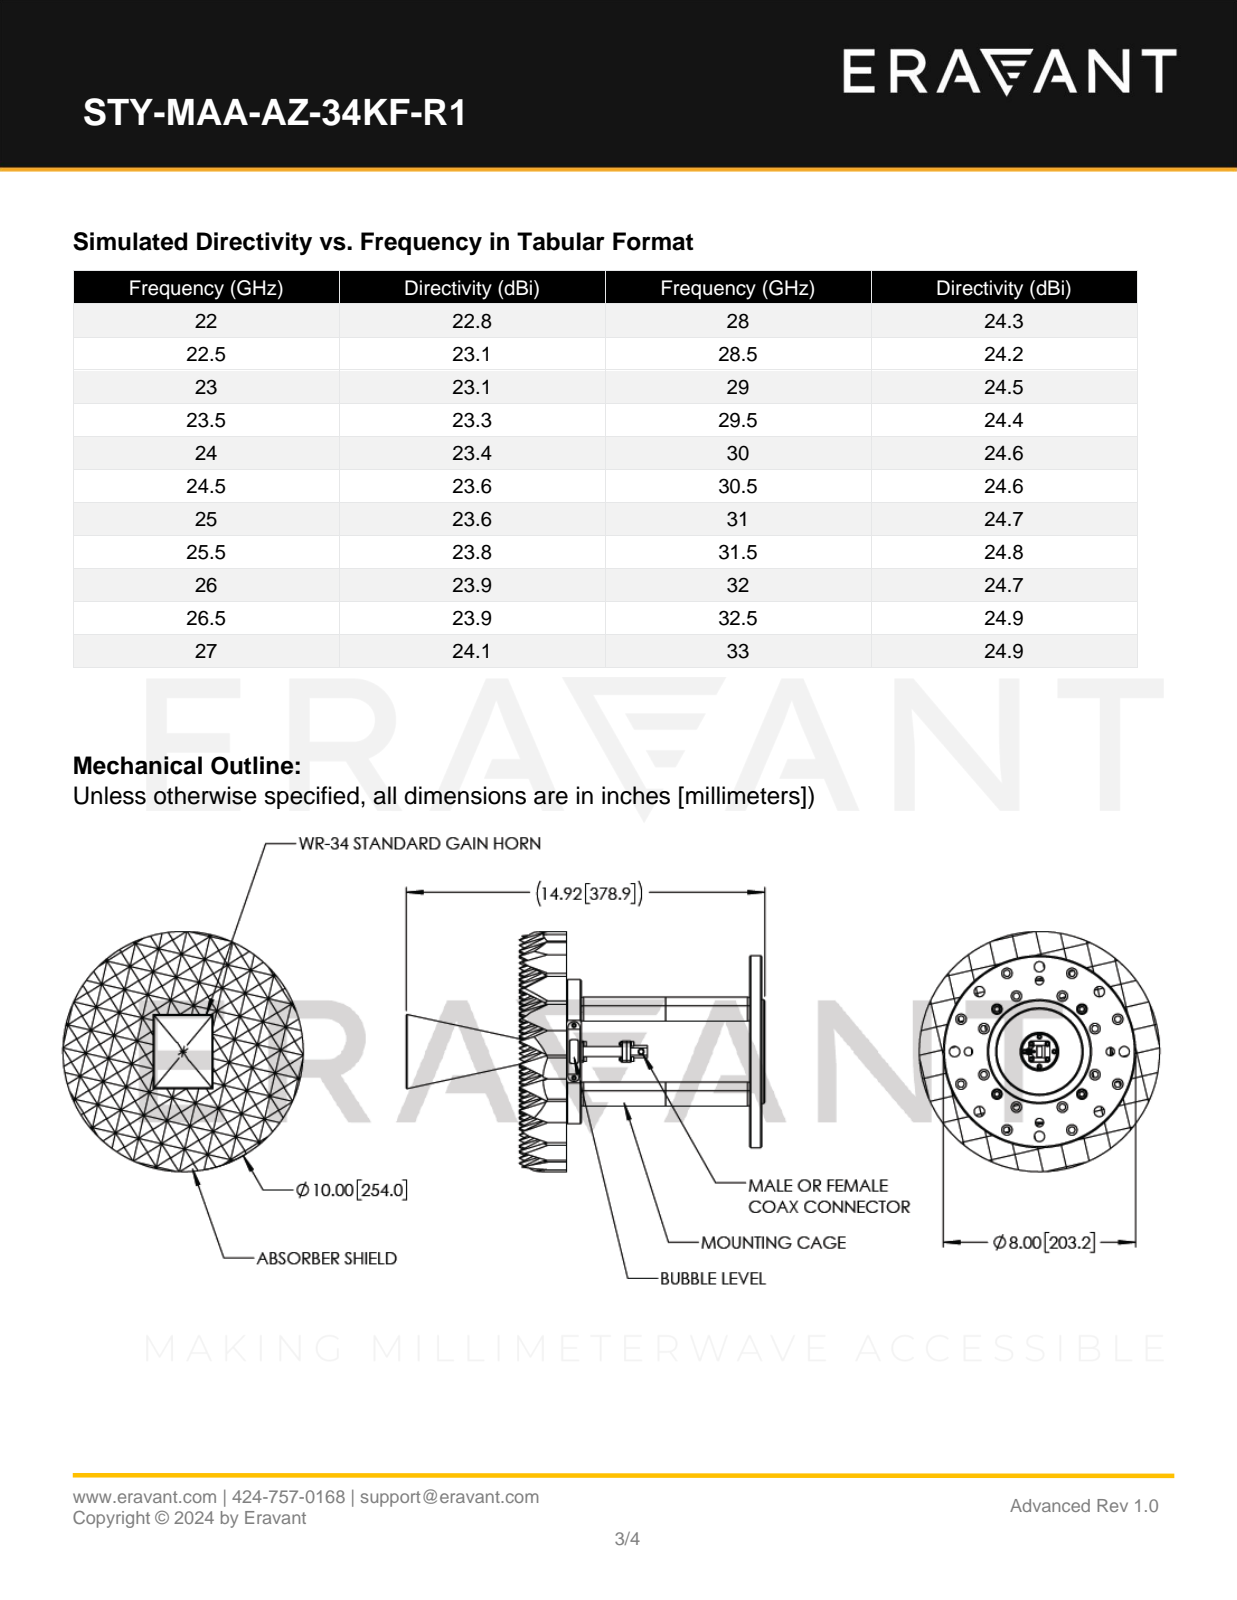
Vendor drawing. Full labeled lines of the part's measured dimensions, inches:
Part name (STEP PRODUCT): STY-MAA-AZ-28KF-R1
STEP written by: SolidWorks 2021 (CONFIG_CONTROL_DESIGN)
Units: inches
Bodies: 84 solids, 1825 faces (700 planar, 458 cylindrical, 667 other)
Overall size (bounding box): 13.823 × 10 × 10
Volume: 161.8 in³ · Surface area: 791.1 in²
Round holes (diameter × count): ⌀0.266 ×20, ⌀0.437 ×16, ⌀0.433 ×8, ⌀0.12 ×4, ⌀0.348 ×4, ⌀0.75 ×4, ⌀0.089 ×2, ⌀0.125 ×2, ⌀0.182 ×1, ⌀1.4 ×1, ⌀3.543 ×1
Round bosses / shafts (diameter × count): ⌀0.21 ×5, ⌀1 ×4, ⌀0.437 ×4, ⌀0.183 ×4, ⌀0.112 ×4, ⌀0.08 ×4, ⌀10 ×1, ⌀8 ×1
Partial cylindrical surfaces — rounded edges, fillets, slot ends (radius × count): R0.042 ×4, R0.08 ×2, R0.25 ×2, R0.155 ×1, R0.24 ×1
Main face-to-face distances: 0.984, 1.969, 0.985, 1.969, 2.953, 3.938, 3.937, 2.953, 5.906, 4.922
Hole centre spacings: 4.326, 5.585, 3.458, 5.046, 5.918, 1.551, 2.496, 3.53
